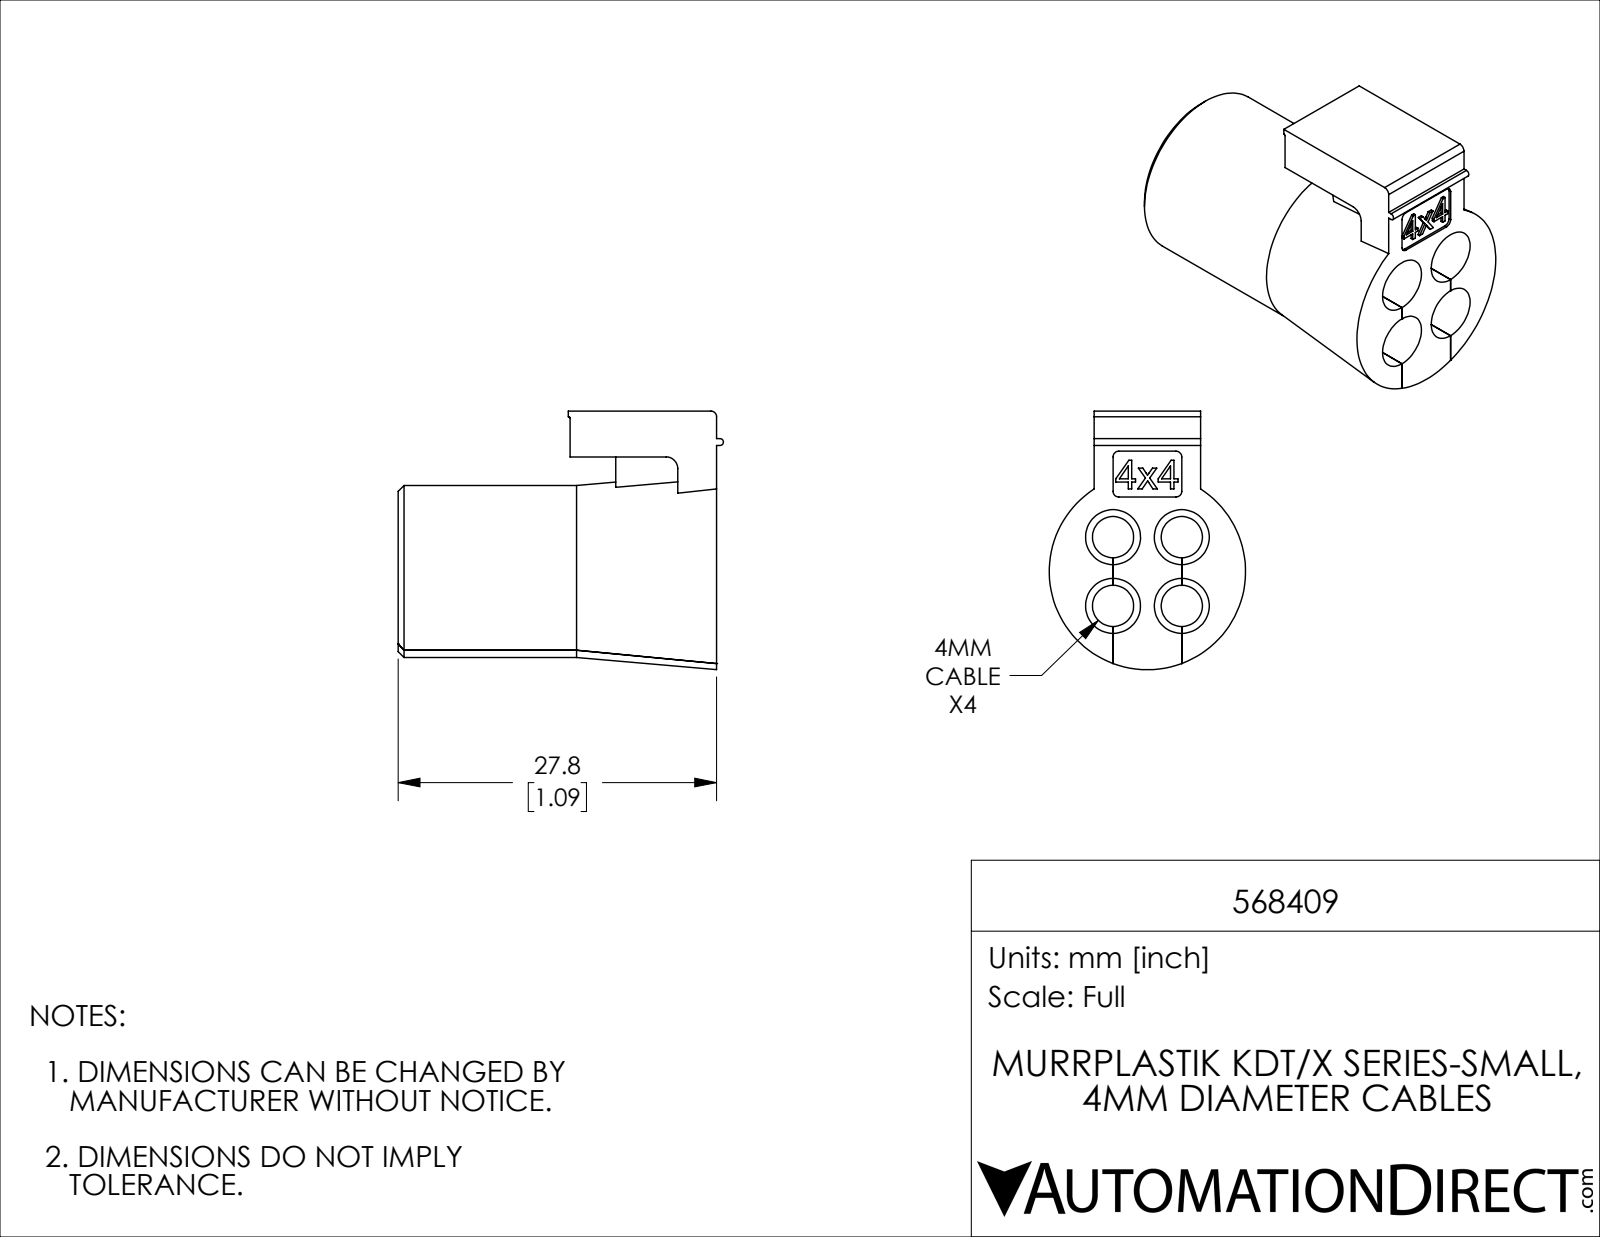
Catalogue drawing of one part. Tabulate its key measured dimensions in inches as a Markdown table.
| quantity | value |
| --- | --- |
| part name | 568409 |
| STEP written by | SolidWorks 2019 (CONFIG_CONTROL_DESIGN) |
| units | inches |
| bodies | 1 solid, 142 faces (76 planar, 40 cylindrical, 26 other) |
| overall size | 1.118 × 0.889 × 0.675 |
| volume | 0.235 in³ |
| surface area | 6.24 in² |
| round holes (diameter × count) | 0.142 × 4, 0.189 × 4 |
| round bosses / shafts (diameter × count) | 0.591 × 1 |
| partial cylindrical surfaces (radius × count) | 0.02 × 5, 0.004 × 1, 0.012 × 1, 0.039 × 1 |
| main face-to-face distances | 0.237, 0.065, 0.065, 0.301, 0.302, 0.236, 0.237, 1.094, 0.157, 0.366 |
| hole center spacings | 0.236, 0.334 |
